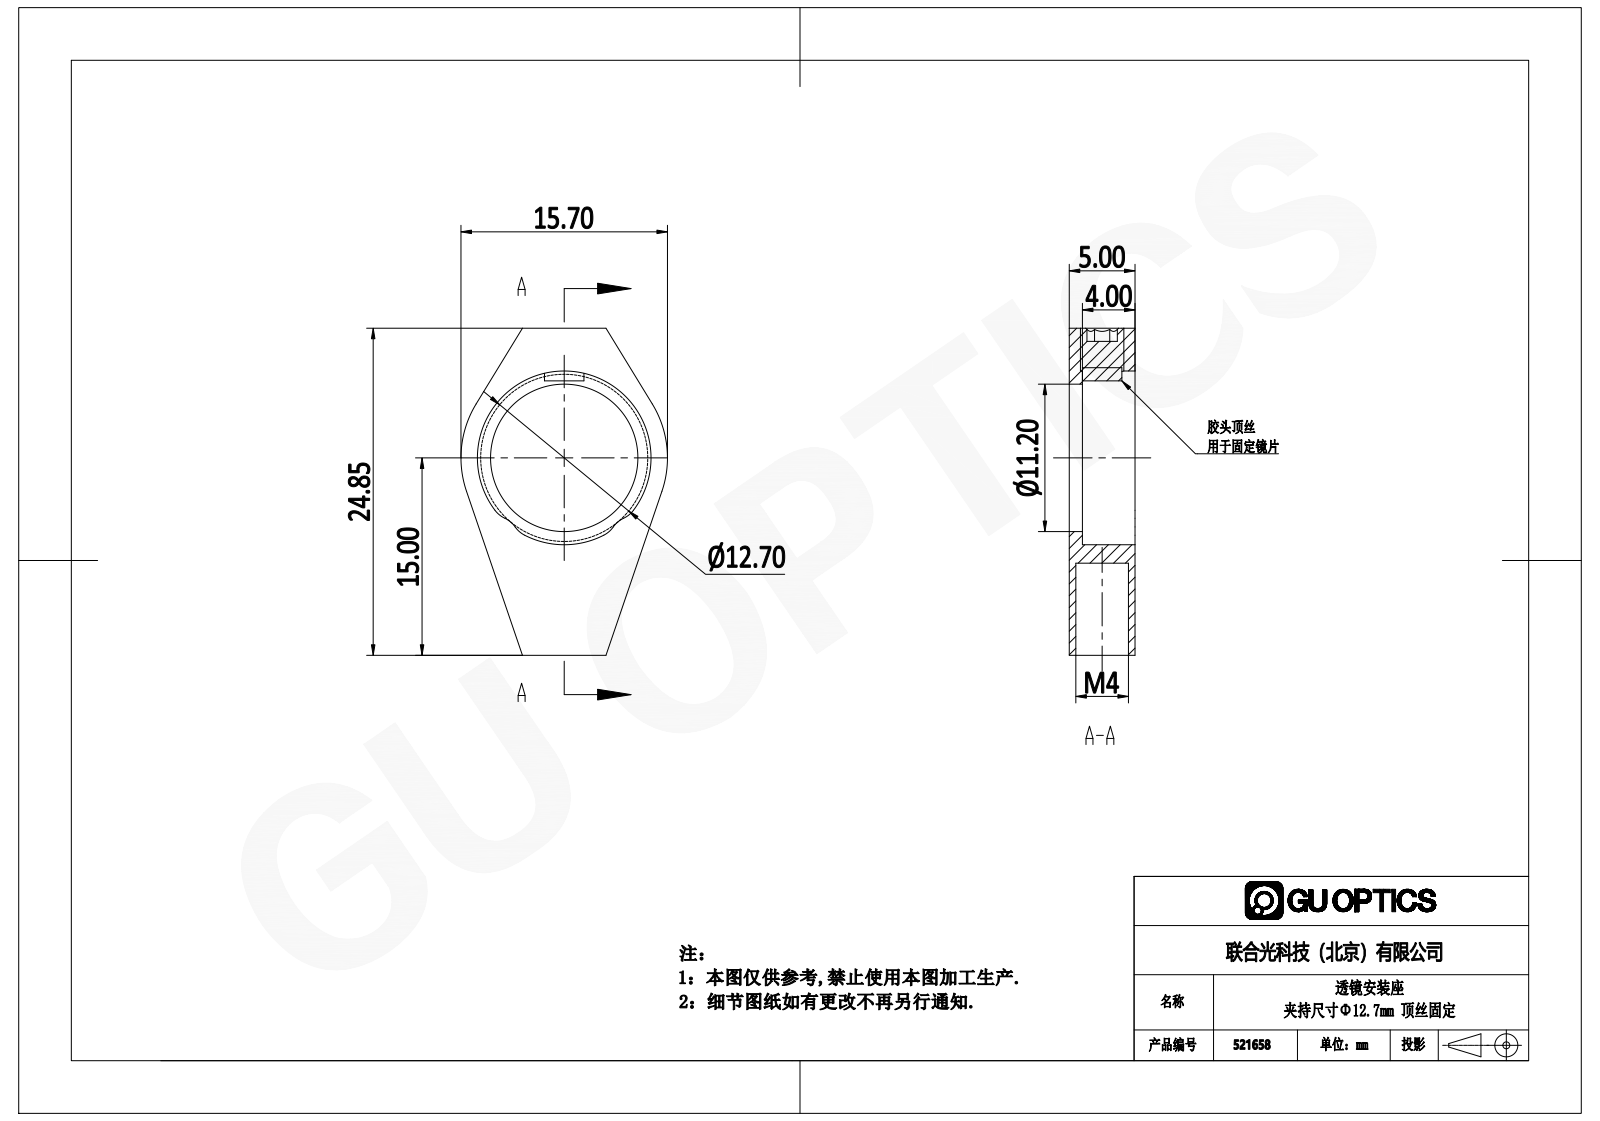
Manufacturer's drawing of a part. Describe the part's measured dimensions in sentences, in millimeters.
The part is named "1.3.1.18_ZZT-0.5-D". Its 3-D file was written by "SolidWorks 2021 (CONFIG_CONTROL_DESIGN)". It is 0 solids with 45 faces: 18 planar, 21 cylindrical and 6 other. Overall it measures 24.85 by 15.7 by 5 millimeters. Round holes: 1 of diameter 3.3, 1 of diameter 4, 1 of diameter 11.2, 1 of diameter 13.2. Round bosses or shafts: 1 of diameter 3. Partial cylindrical surfaces (rounded edges, fillets, slot ends): 6 of radius 2, 1 of radius 7.85. The main face-to-face distances are 5, 4, 1, 24.85, 20.85, 23.85, 3, 2.
